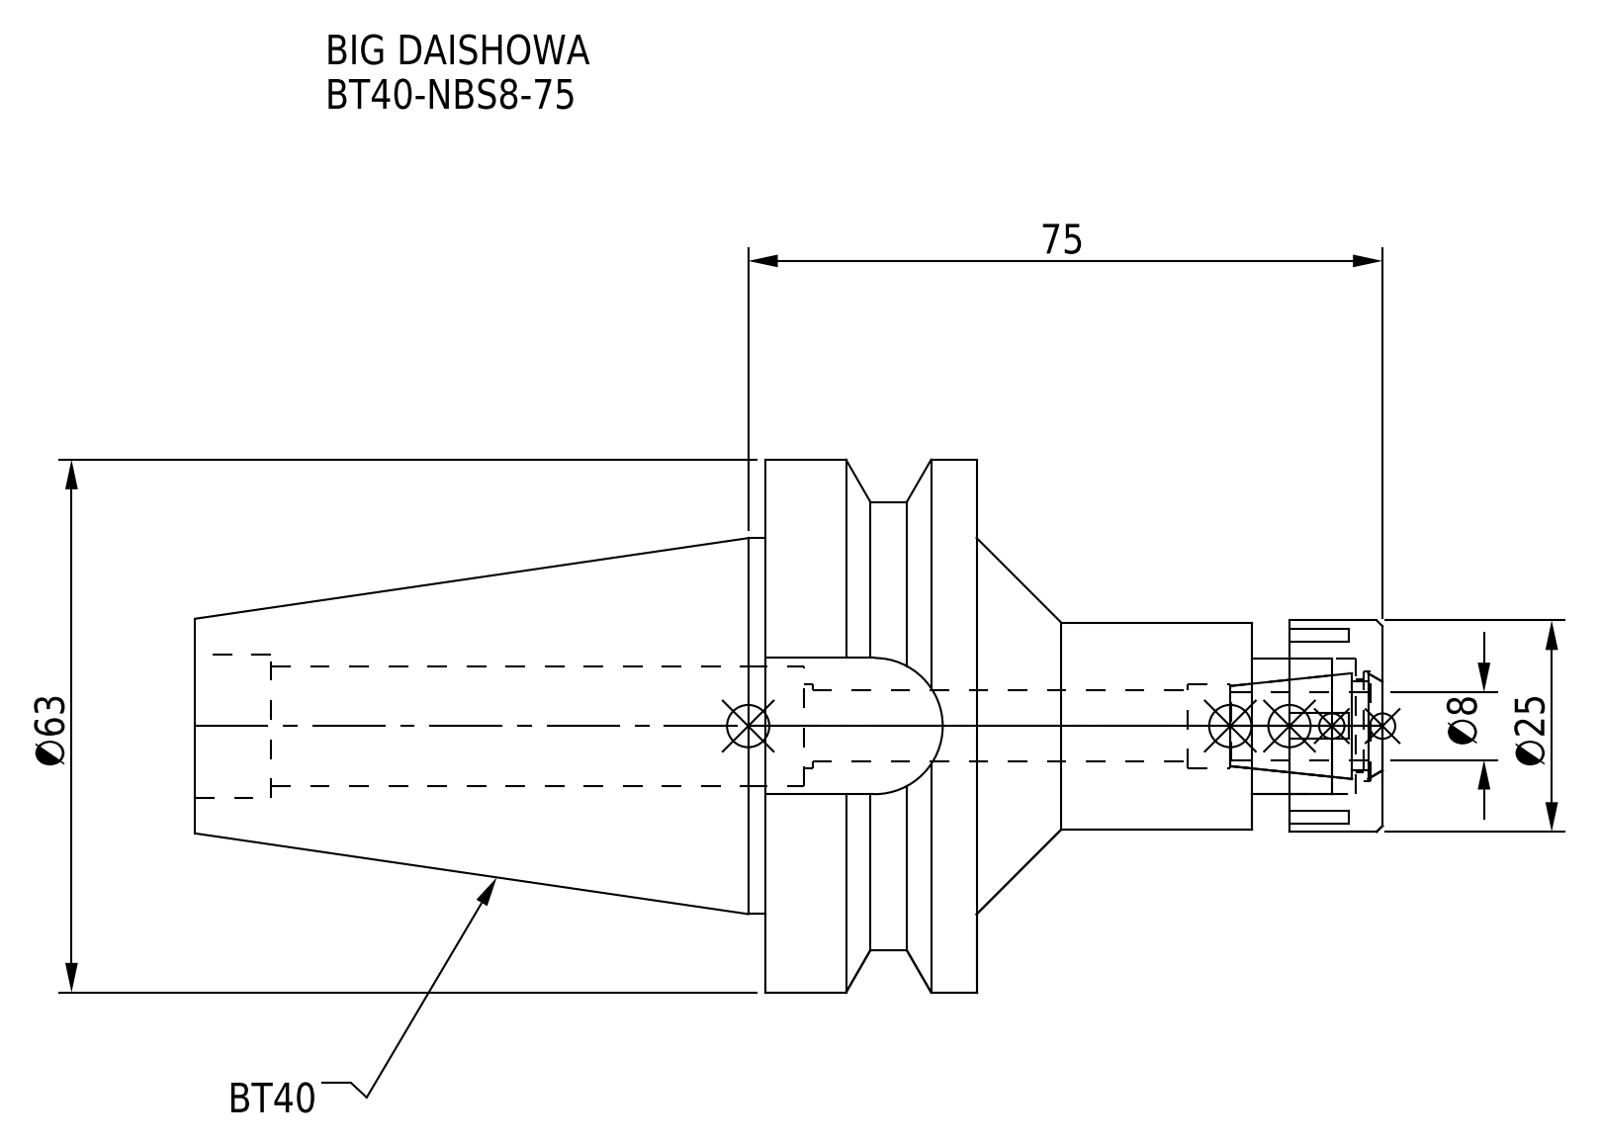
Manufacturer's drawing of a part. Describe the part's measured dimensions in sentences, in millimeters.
The part is named "DXF_TEMP_ASSY_ASM_4_ASM.stp; BT40-NBS8-75.stp; NBN8_1.stp; BT40-NBS8-75_1.stp (+3 more)". Its 3-D file was written by "SolidWorks 2019 (CONFIG_CONTROL_DESIGN)". It is 2 solids with 93 faces: 45 planar, 34 cylindrical and 14 other. Overall it measures 140.4 by 63 by 63 millimeters. Its volume is 143 662 cubic millimeters and its surface area 28 623 square millimeters. Round holes: 1 of diameter 8.4, 1 of diameter 10, 1 of diameter 11, 1 of diameter 13, 1 of diameter 14.2, 1 of diameter 16, 1 of diameter 17. Round bosses or shafts: 1 of diameter 63, 1 of diameter 53, 1 of diameter 44.45, 1 of diameter 25, 1 of diameter 24.5. Partial cylindrical surfaces (rounded edges, fillets, slot ends): 1 of radius 8.05. The main face-to-face distances are 25, 73, 48, 45, 67.4, 140.4, 92.4, 15.5, 32.5, 57.5.
